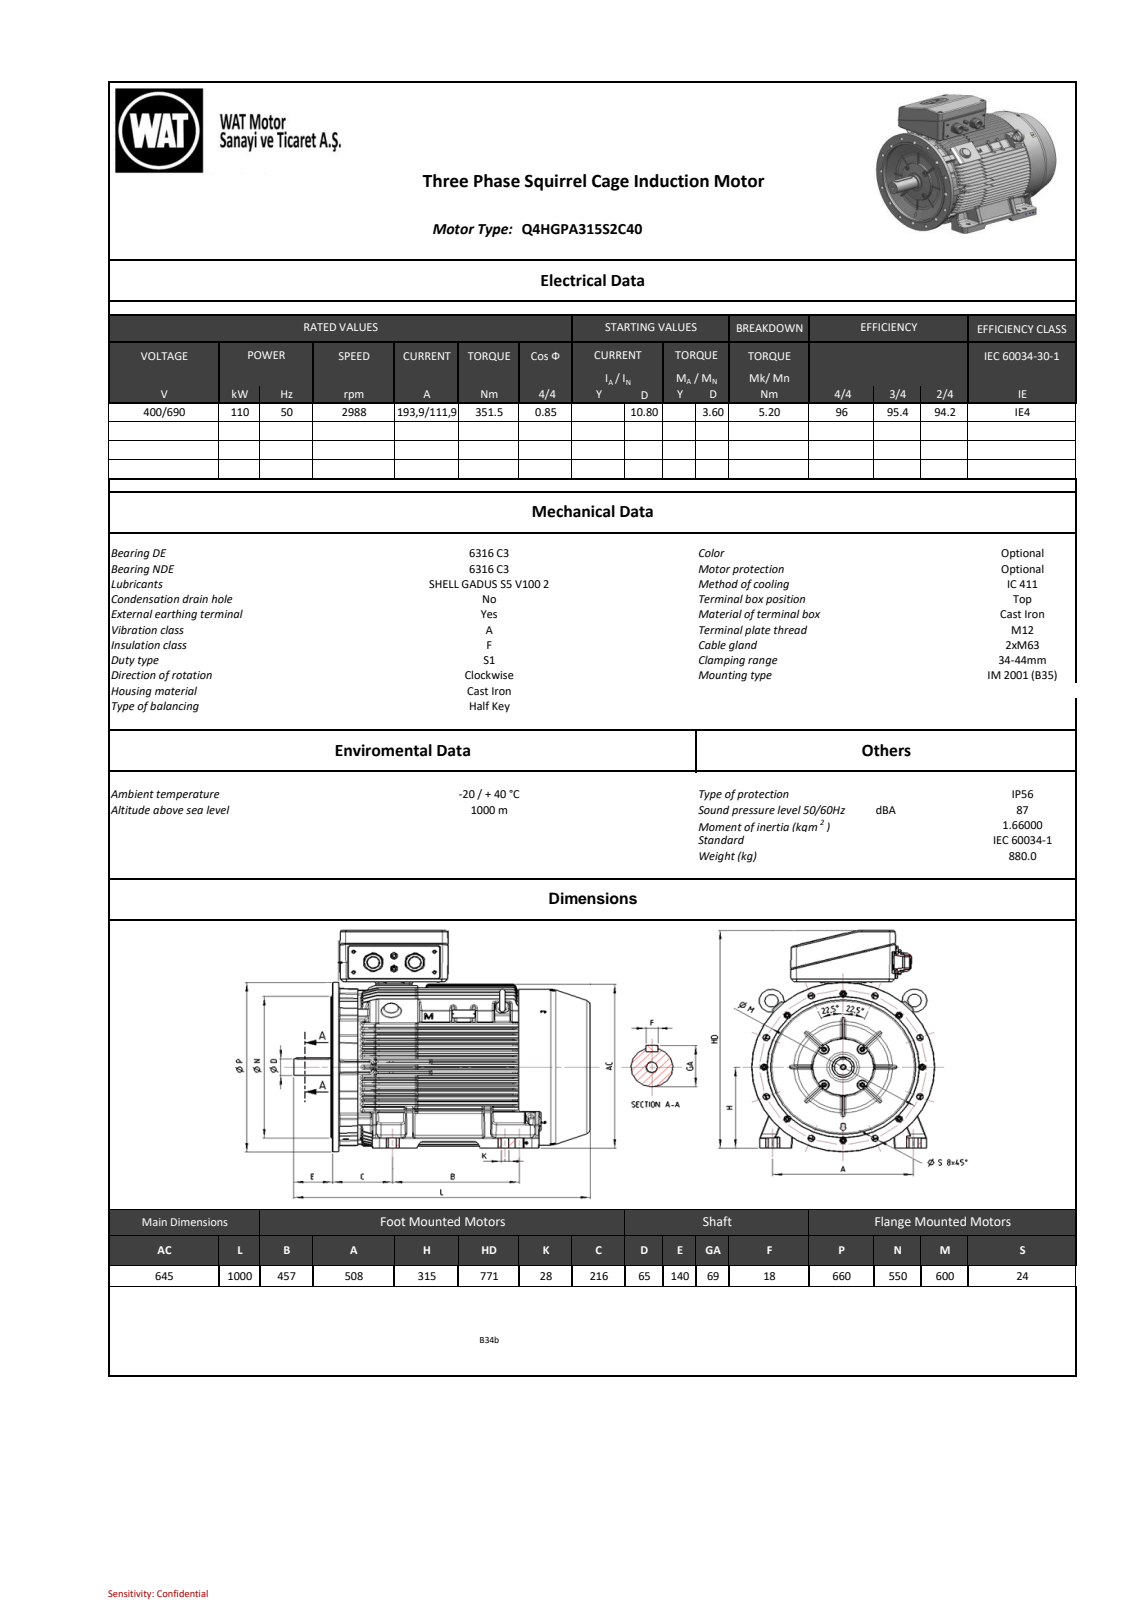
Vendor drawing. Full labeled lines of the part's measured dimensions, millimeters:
Part name (STEP PRODUCT): 26009910674F4pgn
STEP written by: SIEMENS PLM Software NX 11.0 (AUTOMOTIVE_DESIGN)
Units: millimetres
Bodies: 0 solids, 7749 faces (3975 planar, 1449 cylindrical, 2325 other)
Overall size (bounding box): 1000 × 862.37 × 660
Round holes (diameter × count): ⌀24 ×8, ⌀26 ×8, ⌀20 ×5, ⌀8.5 ×4, ⌀8 ×3, ⌀9 ×3, ⌀4 ×2, ⌀12 ×2, ⌀18 ×2, ⌀44 ×2, ⌀44.4 ×2, ⌀44.5 ×2
Round bosses / shafts (diameter × count): ⌀10 ×10, ⌀16 ×8, ⌀20 ×4, ⌀5 ×4, ⌀64.8 ×2, ⌀50 ×2, ⌀660 ×1, ⌀607 ×1
Partial cylindrical surfaces — rounded edges, fillets, slot ends (radius × count): R6 ×632, R3 ×114, R1.5 ×66, R2.09 ×59, R2.61 ×54, R0.8 ×40, R15 ×34, R10 ×28
Main face-to-face distances: 117, 743, 20.8, 263.64, 1.5, 115.5, 858.5, 860, 41.69, 20.89
Hole centre spacings: 486.48, 79.06, 150, 115.07, 115.08, 218.13, 300, 325.24
